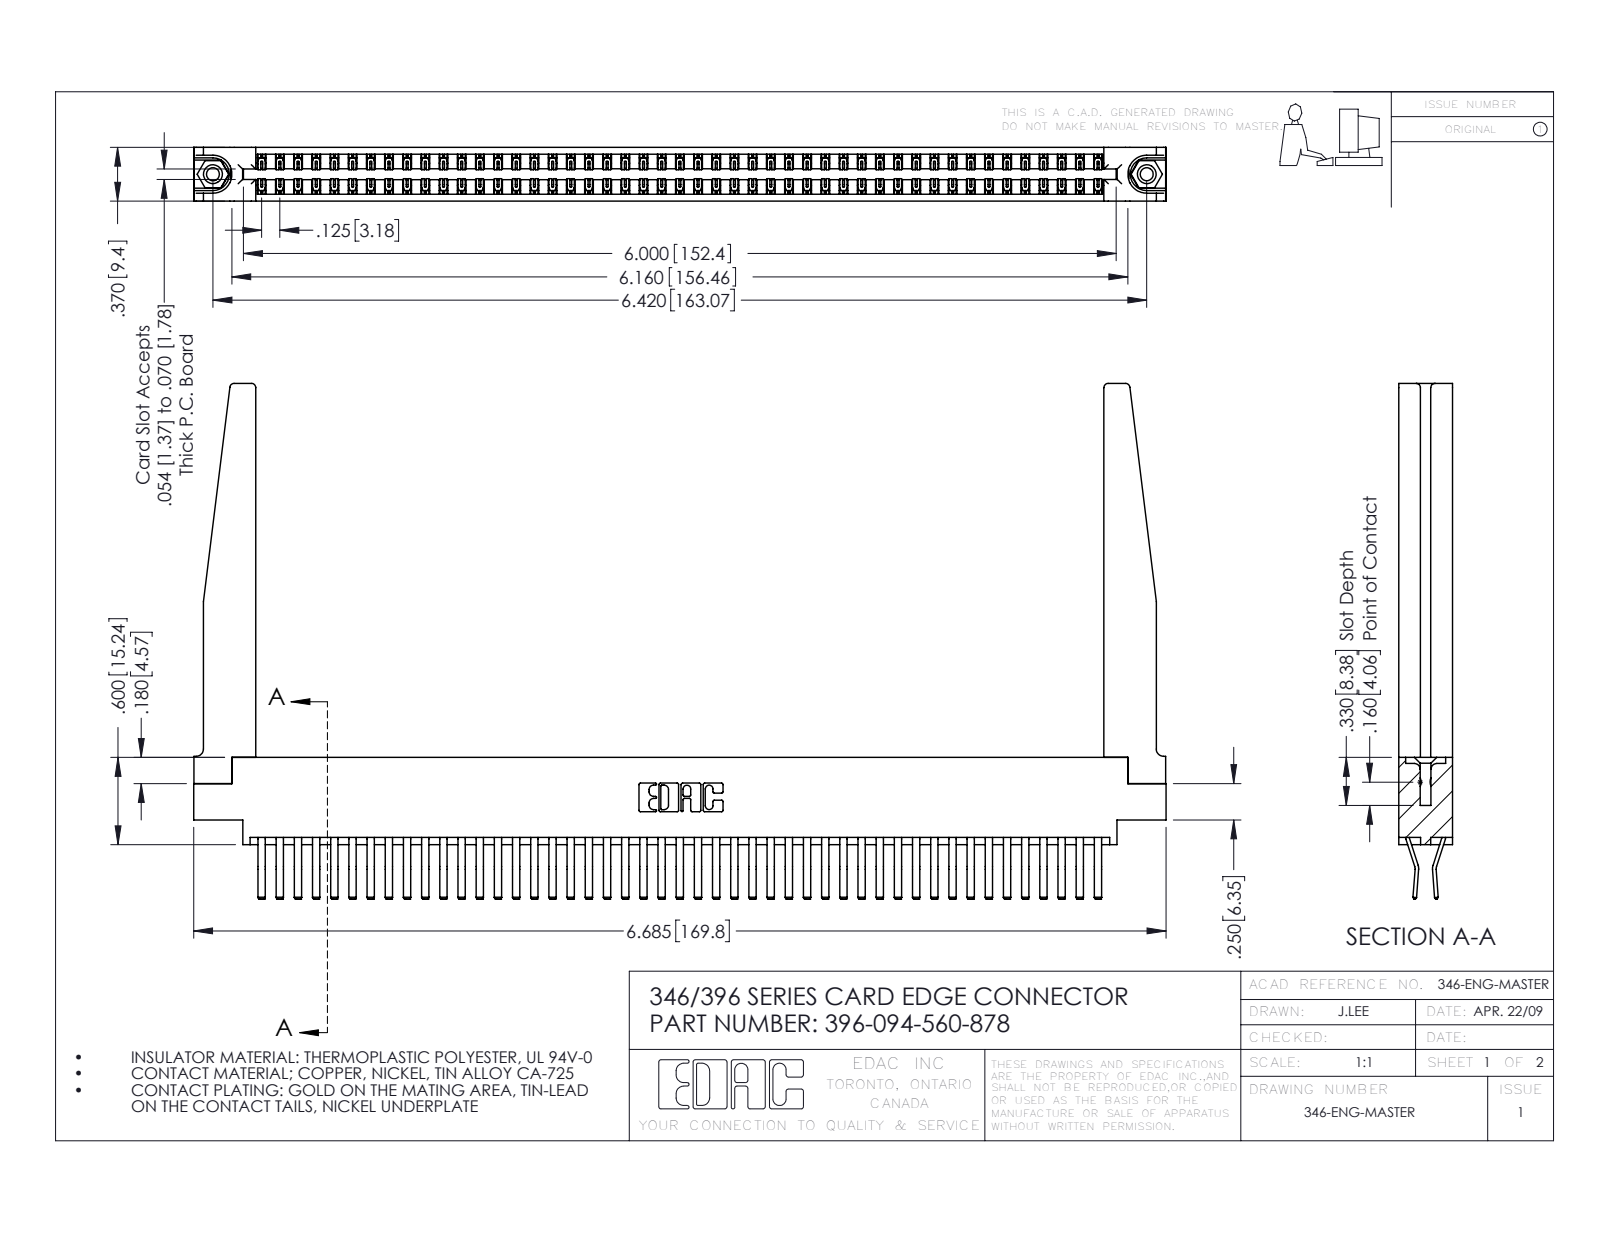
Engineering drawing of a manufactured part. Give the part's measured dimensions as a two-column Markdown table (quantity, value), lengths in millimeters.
| quantity | value |
| --- | --- |
| part name | 346 Part_0.170 Offset - 0.156 Dia-TH; 346-220-078_345-220-078; 345-292-001_560 Tail; 396-094-560-878 (+1 more) |
| STEP written by | SolidWorks 2016 (CONFIG_CONTROL_DESIGN) |
| units | millimeters |
| bodies | 99 solids, 5436 faces (3512 planar, 1872 cylindrical, 52 other) |
| overall size | 169.8 × 90 × 9.4 |
| volume | 23 970 mm³ |
| surface area | 31 880 mm² |
| round holes (diameter × count) | 2.3 × 2, 3.2 × 2, 4 × 2, 1.6 × 1 |
| round bosses / shafts (diameter × count) | 3.9 × 2 |
| partial cylindrical surfaces (radius × count) | 0.2 × 141, 0.3 × 22, 0.8 × 8, 0.2 × 6, 0.8 × 6, 1.3 × 4, 0.7 × 3, 0.3 × 2 |
| main face-to-face distances | 9.4, 1.2, 8.2, 0.6, 1.8, 3.8, 3.8, 6.4, 7.6, 7 |
| hole center spacings | 6.2, 157.8, 163.1 |
